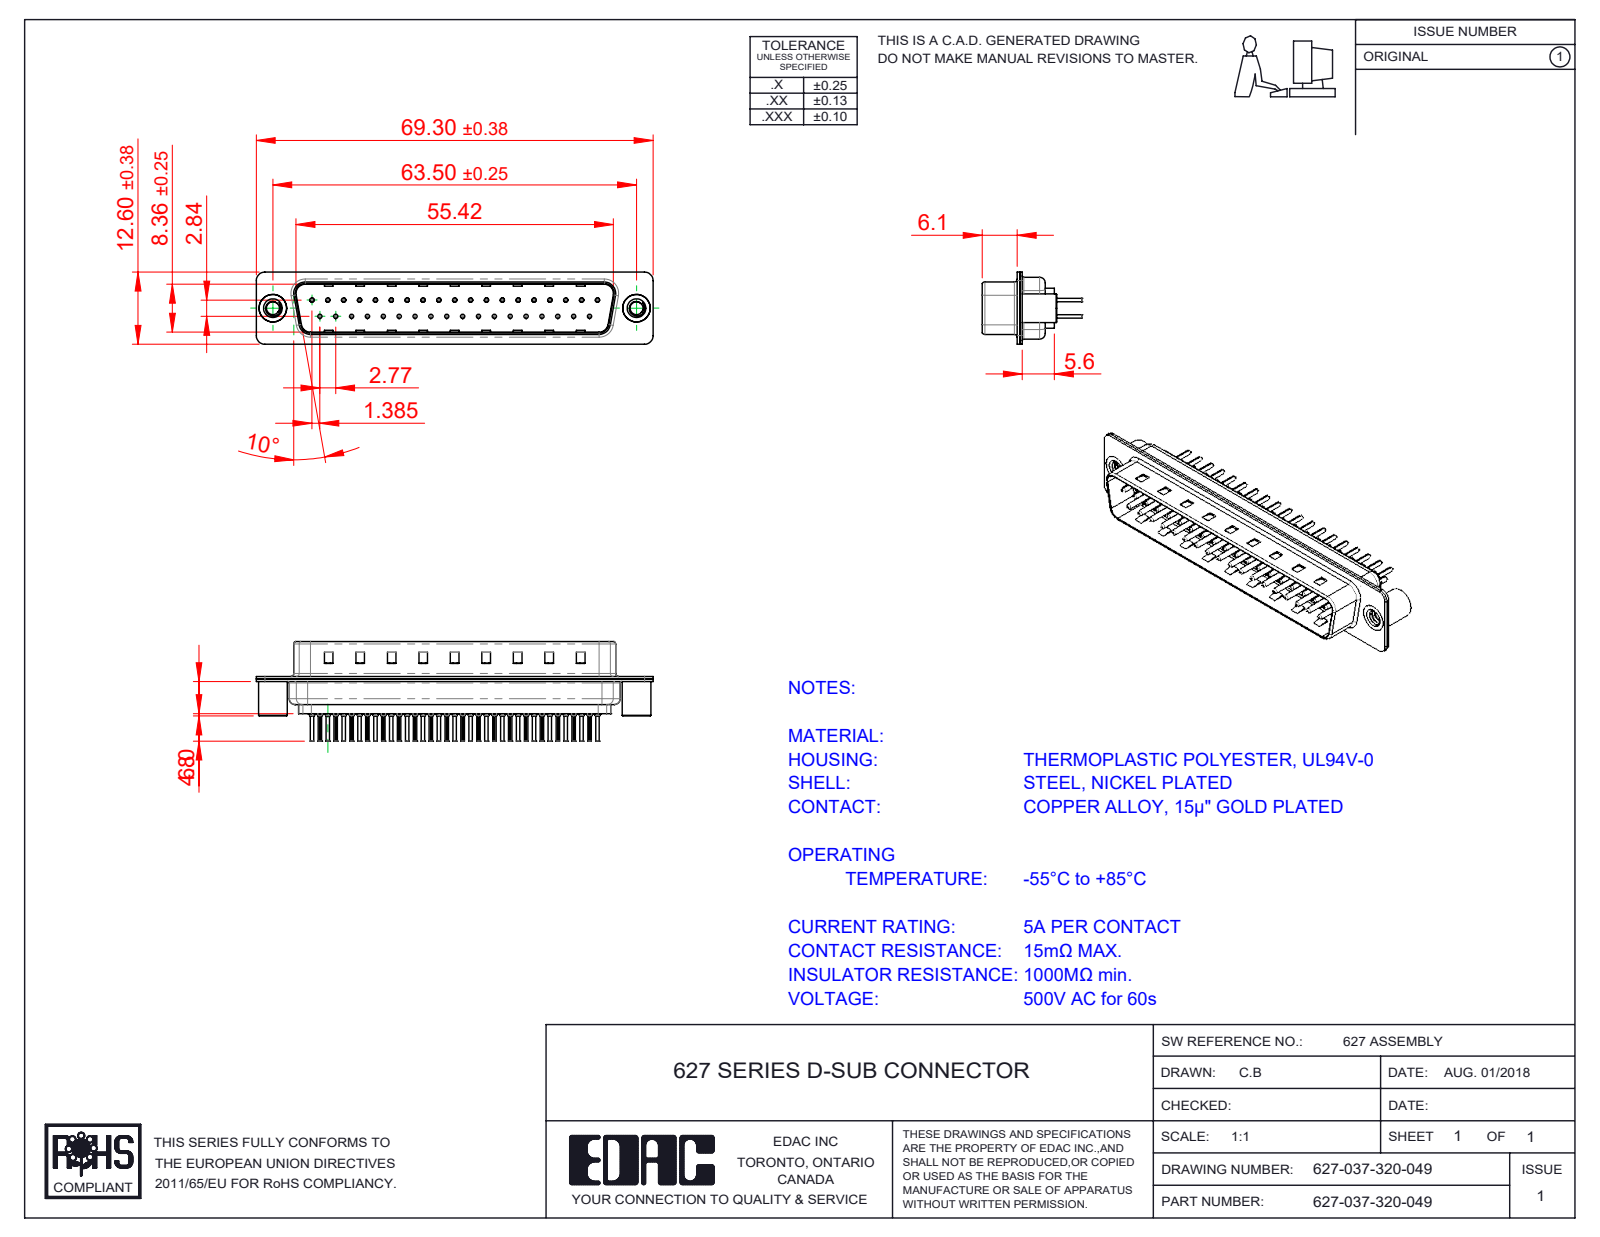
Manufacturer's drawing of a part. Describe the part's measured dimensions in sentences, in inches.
The part is named "627 Contact Row 2_20L; 627 Shell Rear_37 Contacts; 627 Contact Row 1_20L; 627 Shell Front_37 Contacts (+3 more)". Its 3-D file was written by "SolidWorks 2020 (CONFIG_CONTROL_DESIGN)". It is 42 solids with 4060 faces: 1091 planar, 1530 cylindrical and 1439 other. Overall it measures 2.728 by 0.681 by 0.496 inches. Its volume is 0.232 cubic inches and its surface area 16.85 square inches. Round holes: 37 of diameter 0.008, 37 of diameter 0.014, 37 of diameter 0.043, 37 of diameter 0.063, 2 of diameter 0.089, 2 of diameter 0.157, 2 of diameter 0.189. Round bosses or shafts: 37 of diameter 0.079, 37 of diameter 0.059, 37 of diameter 0.03, 37 of diameter 0.024, 2 of diameter 0.197, 2 of diameter 0.193. Partial cylindrical surfaces (rounded edges, fillets, slot ends): 74 of radius 0.004, 16 of radius 0.059, 12 of radius 0.079, 8 of radius 0.02, 8 of radius 0.063, 4 of radius 0.01, 4 of radius 0.024, 4 of radius 0.026. The main face-to-face distances are 0.016, 0.032, 0.377, 0.018, 0.345, 0.059, 0.035, 0.055, 0.256, 0.238. The hole center spacings are 0.124, 0.109, 0.218, 0.327, 0.198, 0.398, 0.436, 0.503.
